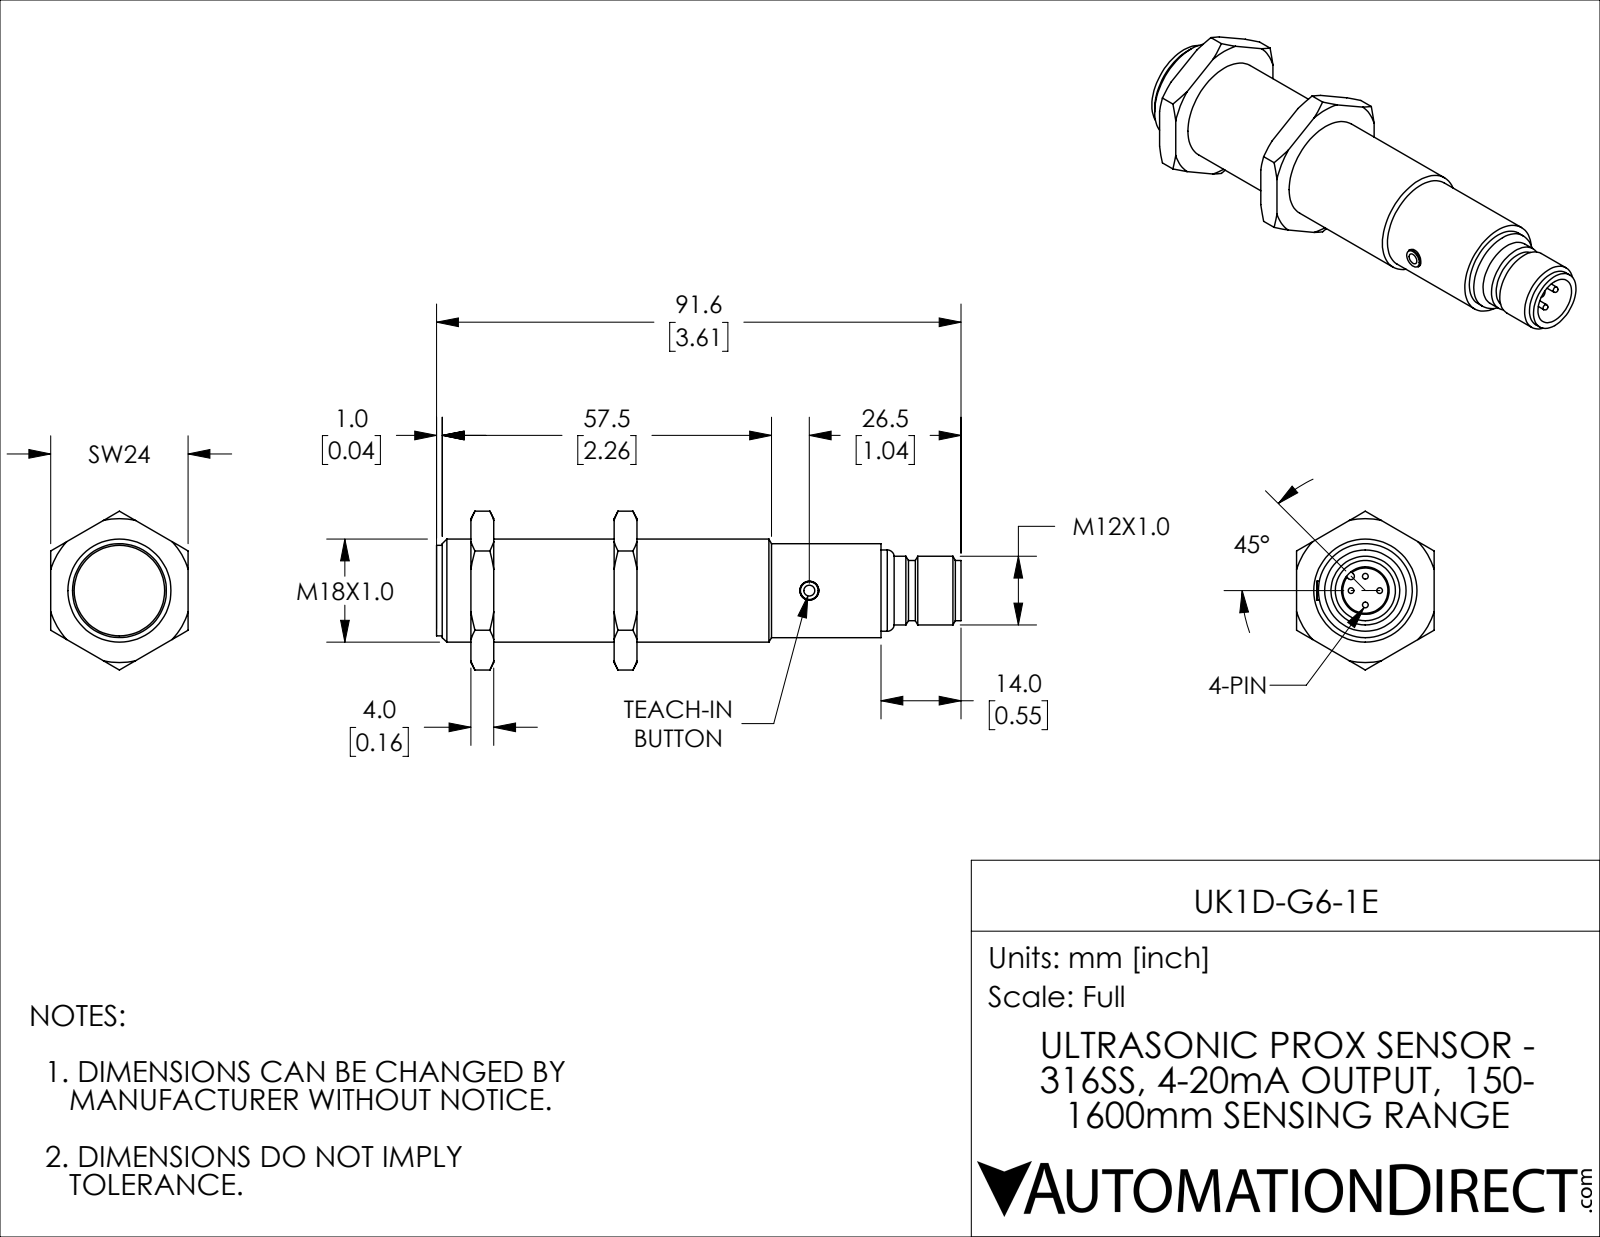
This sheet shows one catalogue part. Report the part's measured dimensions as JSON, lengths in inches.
{"part_name": "UK1D-G6-1E", "step_written_by": "SolidWorks 2018 (AUTOMOTIVE_DESIGN)", "units": "inches", "bodies": {"solids": 4, "faces": 113, "planar": 27, "cylindrical": 35, "other": 51}, "overall_size": [3.606, 1.091, 0.945], "volume_in3": 1.338, "surface_area_in2": 11.97, "round_holes": [[0.13, 1], [0.327, 1], [0.709, 1]], "round_bosses_or_shafts": [[0.039, 4], [0.646, 1], [0.622, 1], [0.559, 1], [0.472, 1], [0.413, 1]], "partial_cylinders_radius": [[0.024, 1]], "face_to_face_distances": [0.984, 0.157, 0.945, 1.142, 0.827, 0.236, 0.394, 1.22, 1.378, 3.055]}
